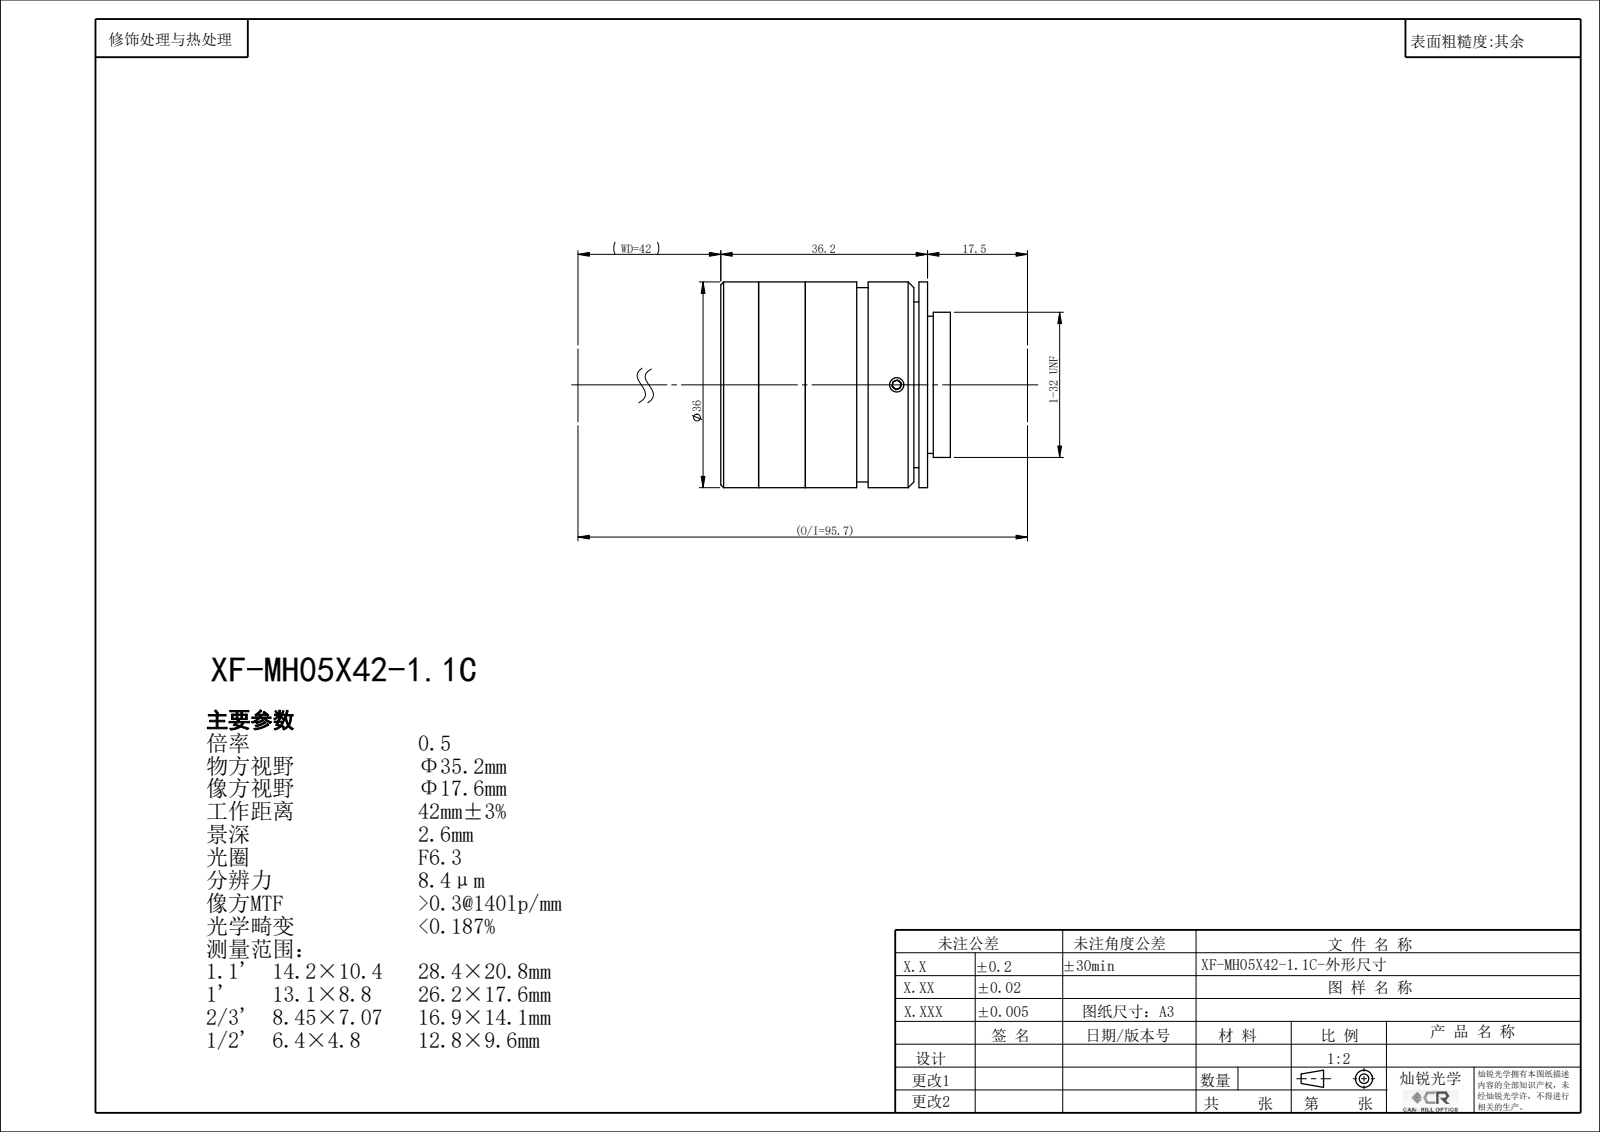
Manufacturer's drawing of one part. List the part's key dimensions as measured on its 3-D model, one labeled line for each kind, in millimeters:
Part name (STEP PRODUCT): XF-MH05X42-1.1C
STEP written by: SolidWorks 2022 (CONFIG_CONTROL_DESIGN)
Units: millimetres
Bodies: 0 solids, 99 faces (44 planar, 34 cylindrical, 21 other)
Overall size (bounding box): 40.2 × 36 × 36
Round holes (diameter × count): ⌀2.5 ×3, ⌀10 ×1, ⌀15 ×1, ⌀17.4 ×1, ⌀21.5 ×1, ⌀24.9 ×1, ⌀26 ×1
Round bosses / shafts (diameter × count): ⌀36 ×1, ⌀34 ×1, ⌀25.4 ×1, ⌀24 ×1
Main face-to-face distances: 29.58, 6.62, 36.2, 14.81, 8.19, 21.39, 1.5, 34.7, 28.08, 19.89
